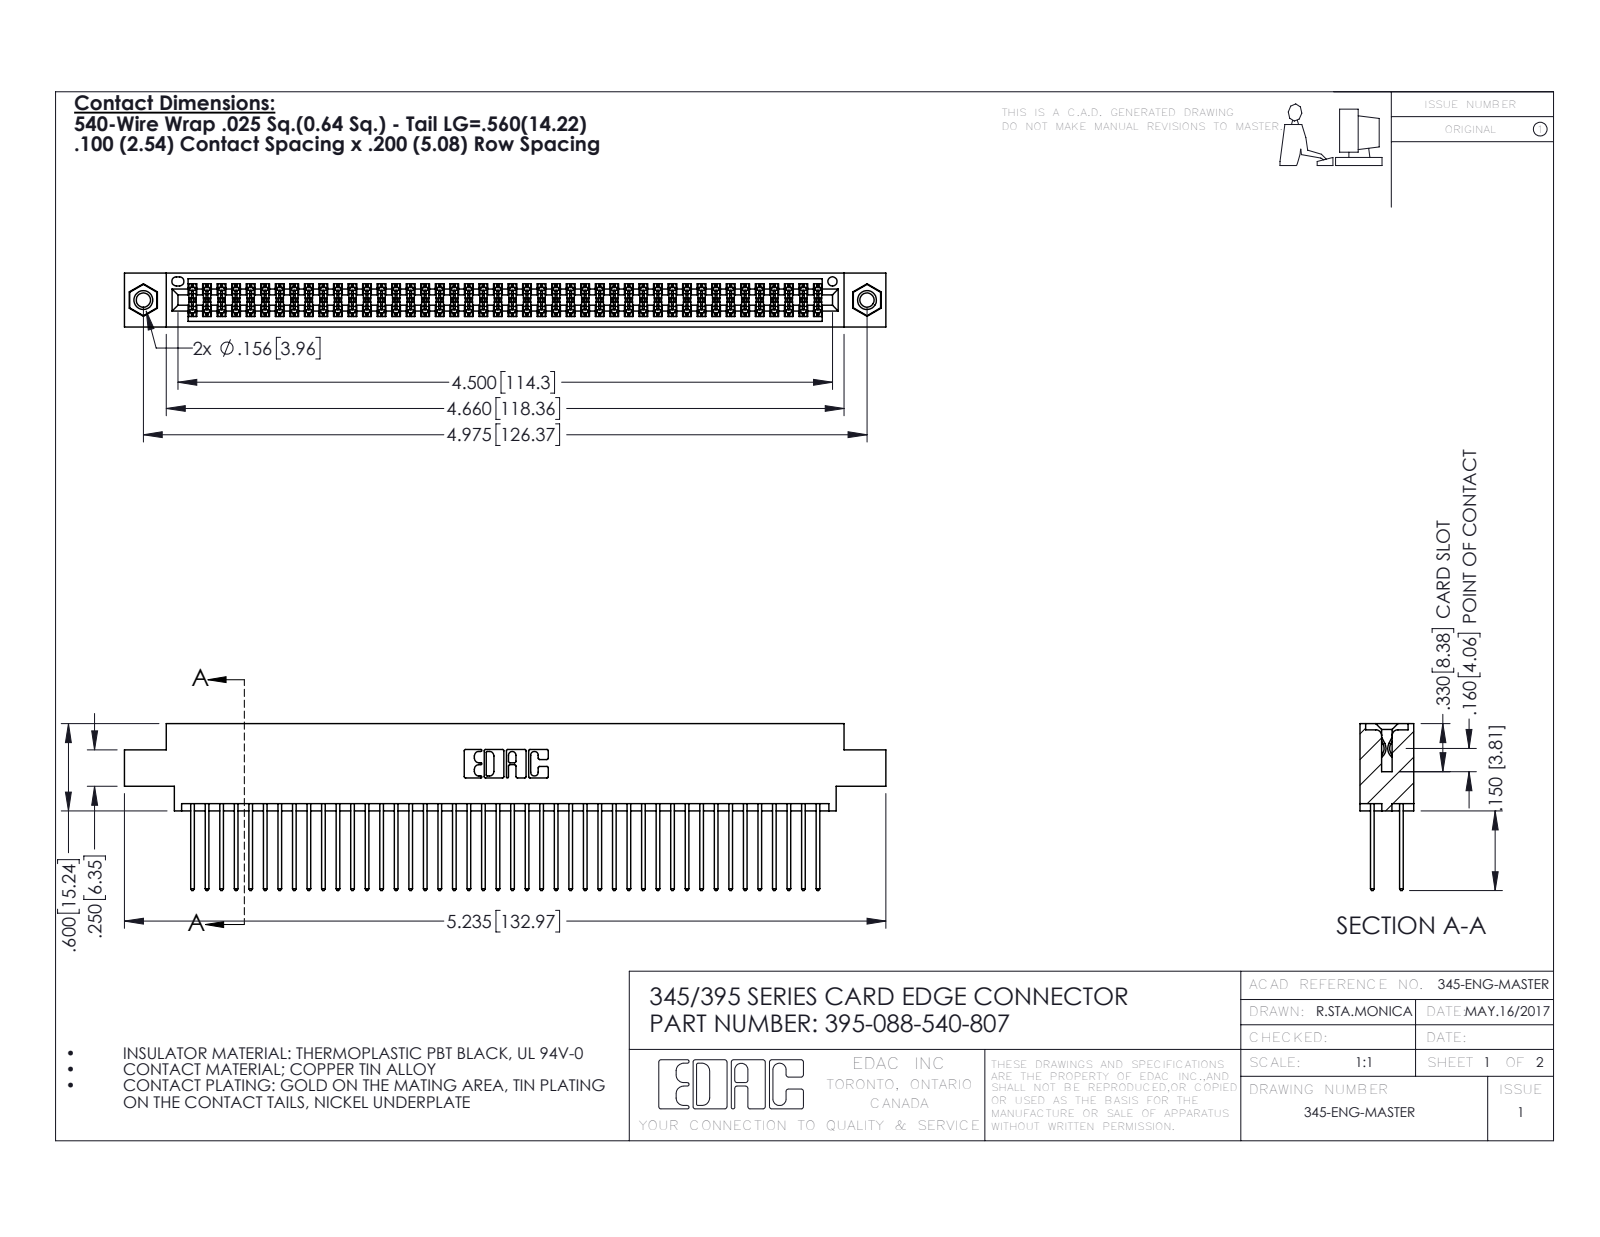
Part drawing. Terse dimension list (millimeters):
name: 345 Part_0.170 Offset - 0.156 Dia-TI; 345-250-001_345-250-005-103; 345-292-001_345-293-140; 395-088-540-807
written by: SolidWorks 2016 (CONFIG_CONTROL_DESIGN)
unit: mm
bodies: 91 solids, 4590 faces (3020 planar, 1554 cylindrical, 16 other)
size: 133 × 29.1 × 9.4
volume: 13 100 mm³; area: 21 190 mm²
holes: 2× ⌀2.5, 2× ⌀3.2, 2× ⌀4, 1× ⌀1.6
bosses: 2× ⌀3.9
rounds: 132× R0.2, 88× R0.3, 22× R0.3, 6× R0.2, 6× R0.8, 3× R0.7, 2× R0.4, 2× R0.5
face distances: 1.8, 7.6, 5.1, 2.5, 6.9, 0.6, 9.4, 5.7, 4.4, 3.8
hole spacings: 6.9, 120.4, 126.4
